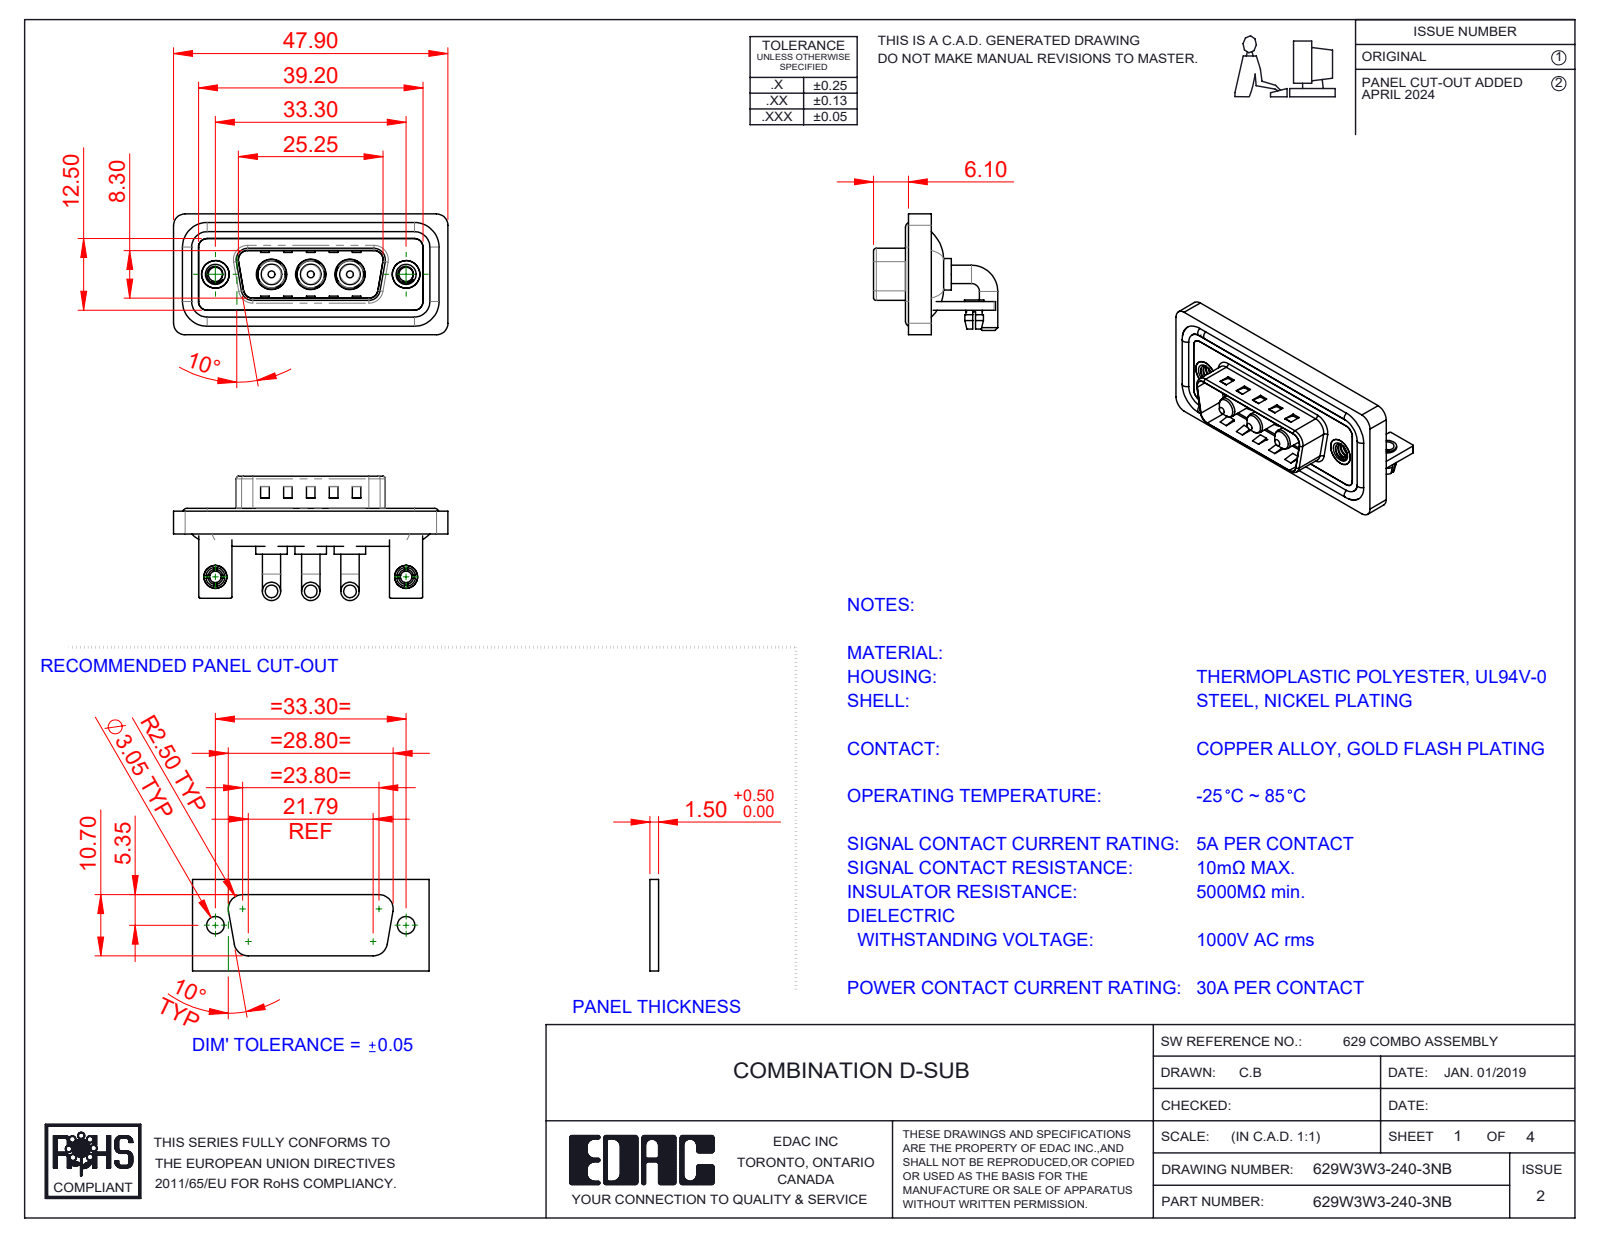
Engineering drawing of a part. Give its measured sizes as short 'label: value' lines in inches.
name: Power Pin_30A RA; 629W3W3-240-3NB; 629Combo Shell Rear_15 Contacts; 629Combo Stabilizer Bracket (+5 more)
written by: SolidWorks 2023 (CONFIG_CONTROL_DESIGN)
unit: in
bodies: 17 solids, 706 faces (275 planar, 297 cylindrical, 134 other)
size: 1.886 × 0.854 × 0.831
volume: 0.377 in³; area: 15.33 in²
holes: 4× ⌀0.098, 3× ⌀0.191, 3× ⌀0.209, 2× ⌀0.079, 2× ⌀0.126, 2× ⌀0.157, 2× ⌀0.189, 2× ⌀0.197
bosses: 6× ⌀0.126, 4× ⌀0.063, 3× ⌀0.217, 3× ⌀0.205, 3× ⌀0.187, 3× ⌀0.148, 3× ⌀0.142, 2× ⌀0.193
rounds: 21× R0.079, 18× R0.059, 16× R0.01, 9× R0.02, 8× R0.063, 4× R0.024, 4× R0.026, 4× R0.035
face distances: 0.016, 0.059, 0.031, 0.114, 0.043, 0.083, 0.146, 0.063, 0.047, 0.177
hole spacings: 0.27, 0.386, 0.656, 0.925, 1.311, 0.539
